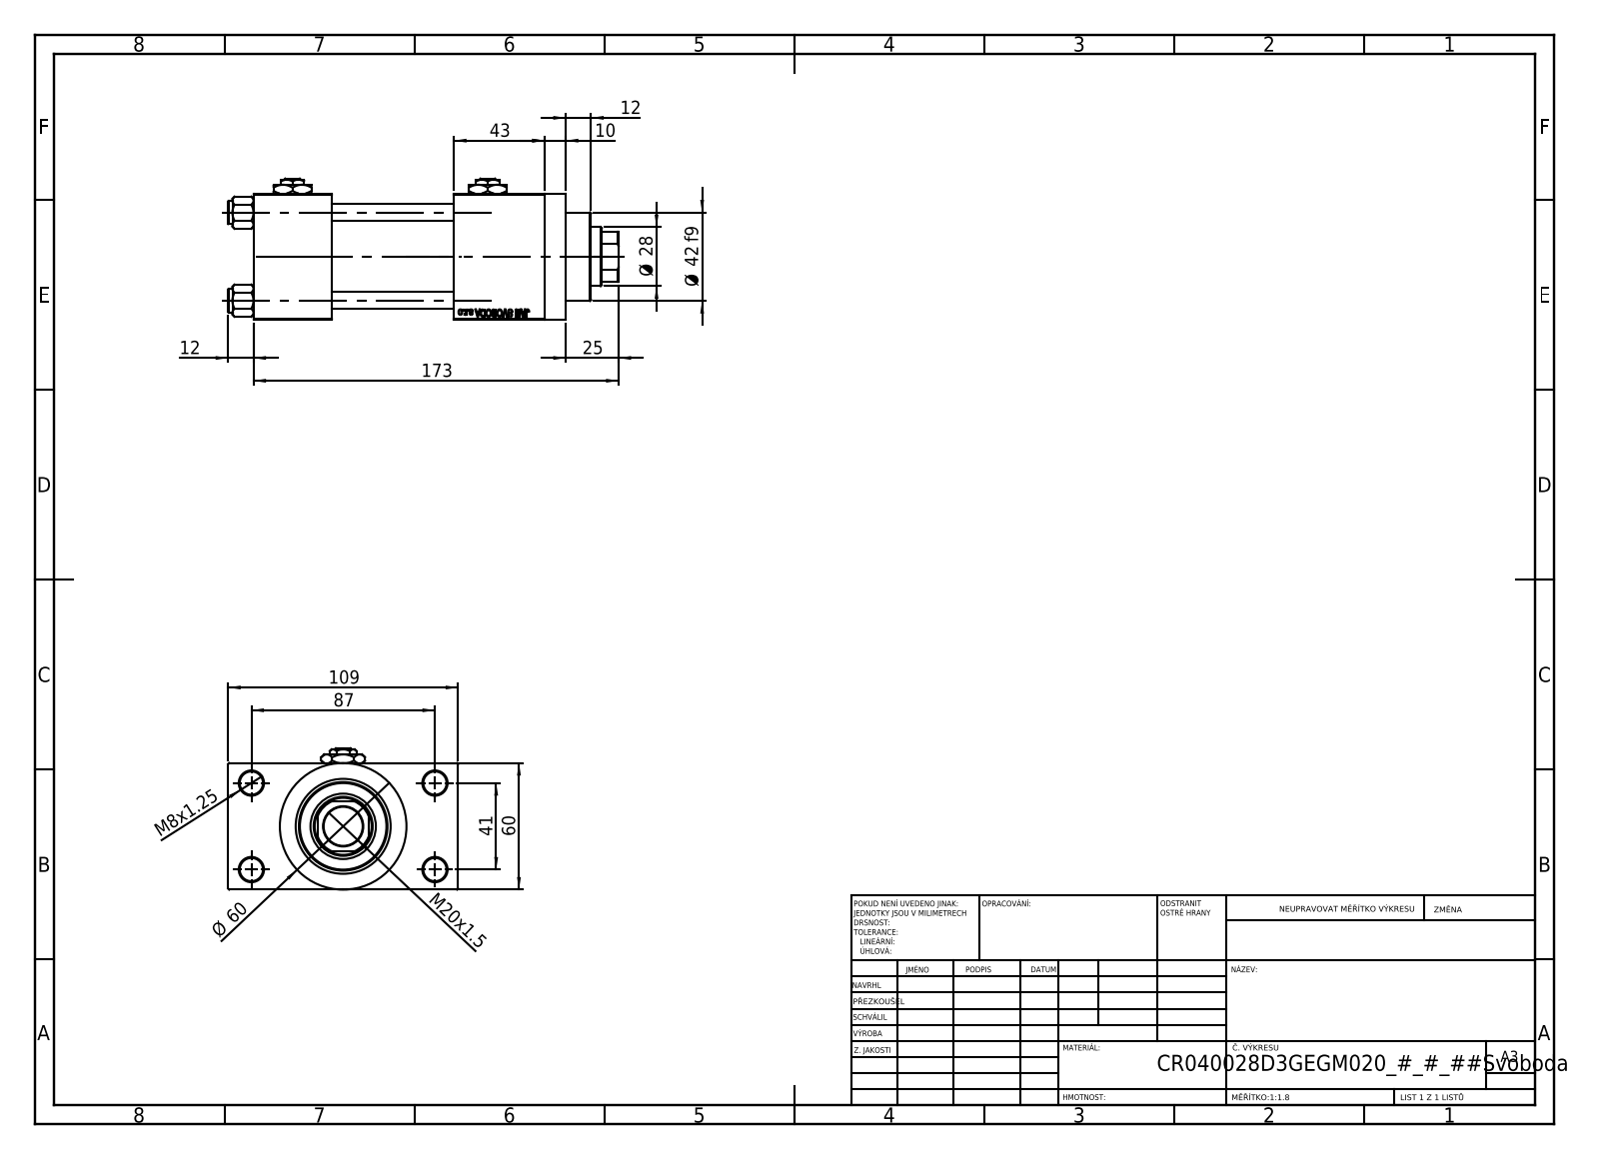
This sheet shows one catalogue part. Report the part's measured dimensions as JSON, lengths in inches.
{"part_name": "V215_VC_A; V215CR_VCP_D; V215CR_D_TYCINKA; NUT_M5_D (+2 more)", "step_written_by": "SolidWorks 2019 (CONFIG_CONTROL_DESIGN)", "units": "inches", "bodies": {"solids": 13, "faces": 1206, "planar": 546, "cylindrical": 100, "other": 560}, "overall_size": [7.283, 4.291, 2.638], "volume_in3": 32.46, "surface_area_in2": 202.2, "round_holes": [[0.315, 4], [0.433, 4], [0.276, 2], [0.656, 2], [0.945, 2], [0.728, 1], [1.102, 1], [1.22, 1], [1.575, 1], [1.772, 1]], "round_bosses_or_shafts": [[0.433, 4], [2.362, 1], [1.811, 1], [1.654, 1]], "partial_cylinders_radius": [[0.531, 1]], "face_to_face_distances": [2.362, 3.327, 0.965, 2.283, 1.457, 3.74, 5.433, 3.976, 1.693, 4.291], "hole_center_spacings": [0.892, 1.161, 1.642, 1.856, 1.893, 2.533, 3.011, 1.614]}
